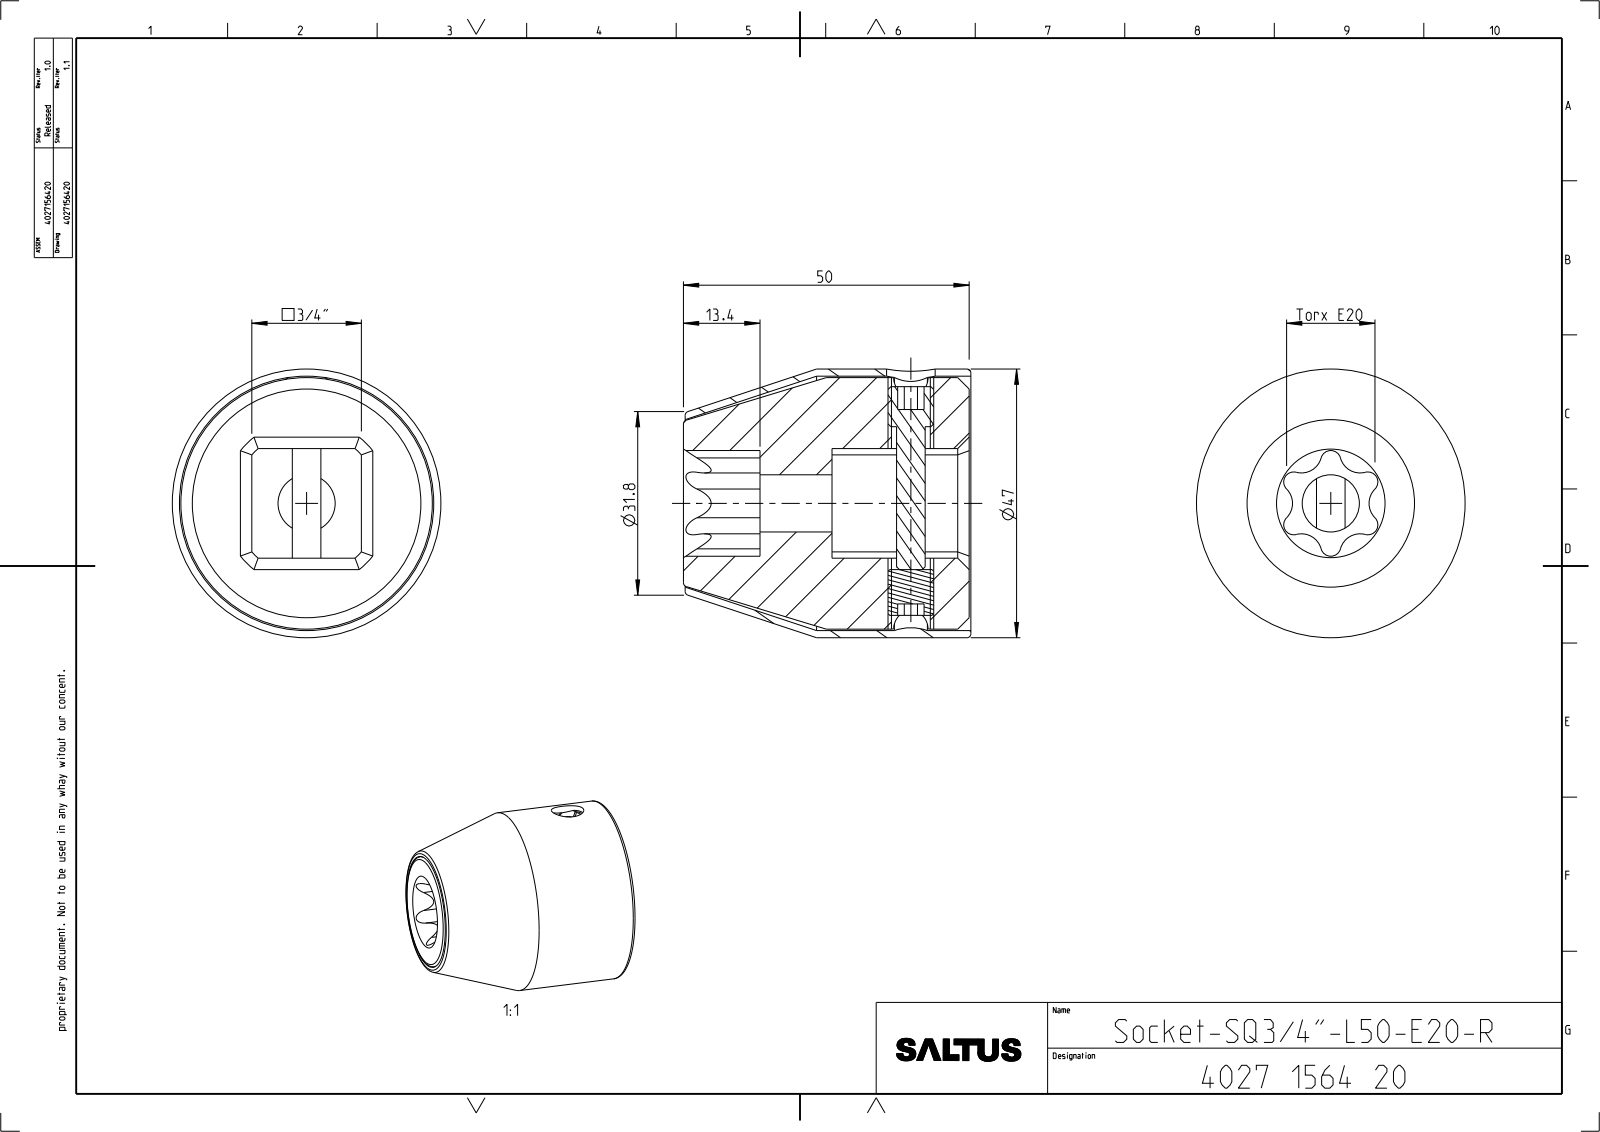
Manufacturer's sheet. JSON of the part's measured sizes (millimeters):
{"part_name": "4027911333; 4027905697; 0190131800_SPEC; 4027043592 (+1 more)", "step_written_by": "CREO PARAMETRIC BY PTC INC, 2022414 (CONFIG_CONTROL_DESIGN)", "units": "millimeters", "bodies": {"solids": 4, "faces": 110, "planar": 33, "cylindrical": 44, "other": 33}, "overall_size": [50.3, 47, 47], "volume_mm3": 58493, "surface_area_mm2": 27071, "round_holes": [[6.8, 1], [8, 1], [8.5, 1], [10, 1], [44.5, 1]], "round_bosses_or_shafts": [[47, 1], [44, 1], [5, 1]], "partial_cylinders_radius": [[1.75, 6], [3.56, 6], [12.8, 1]], "face_to_face_distances": [19.18, 50, 26, 24, 36.6, 12.6, 13.4, 24.3, 36.9, 50.3]}
